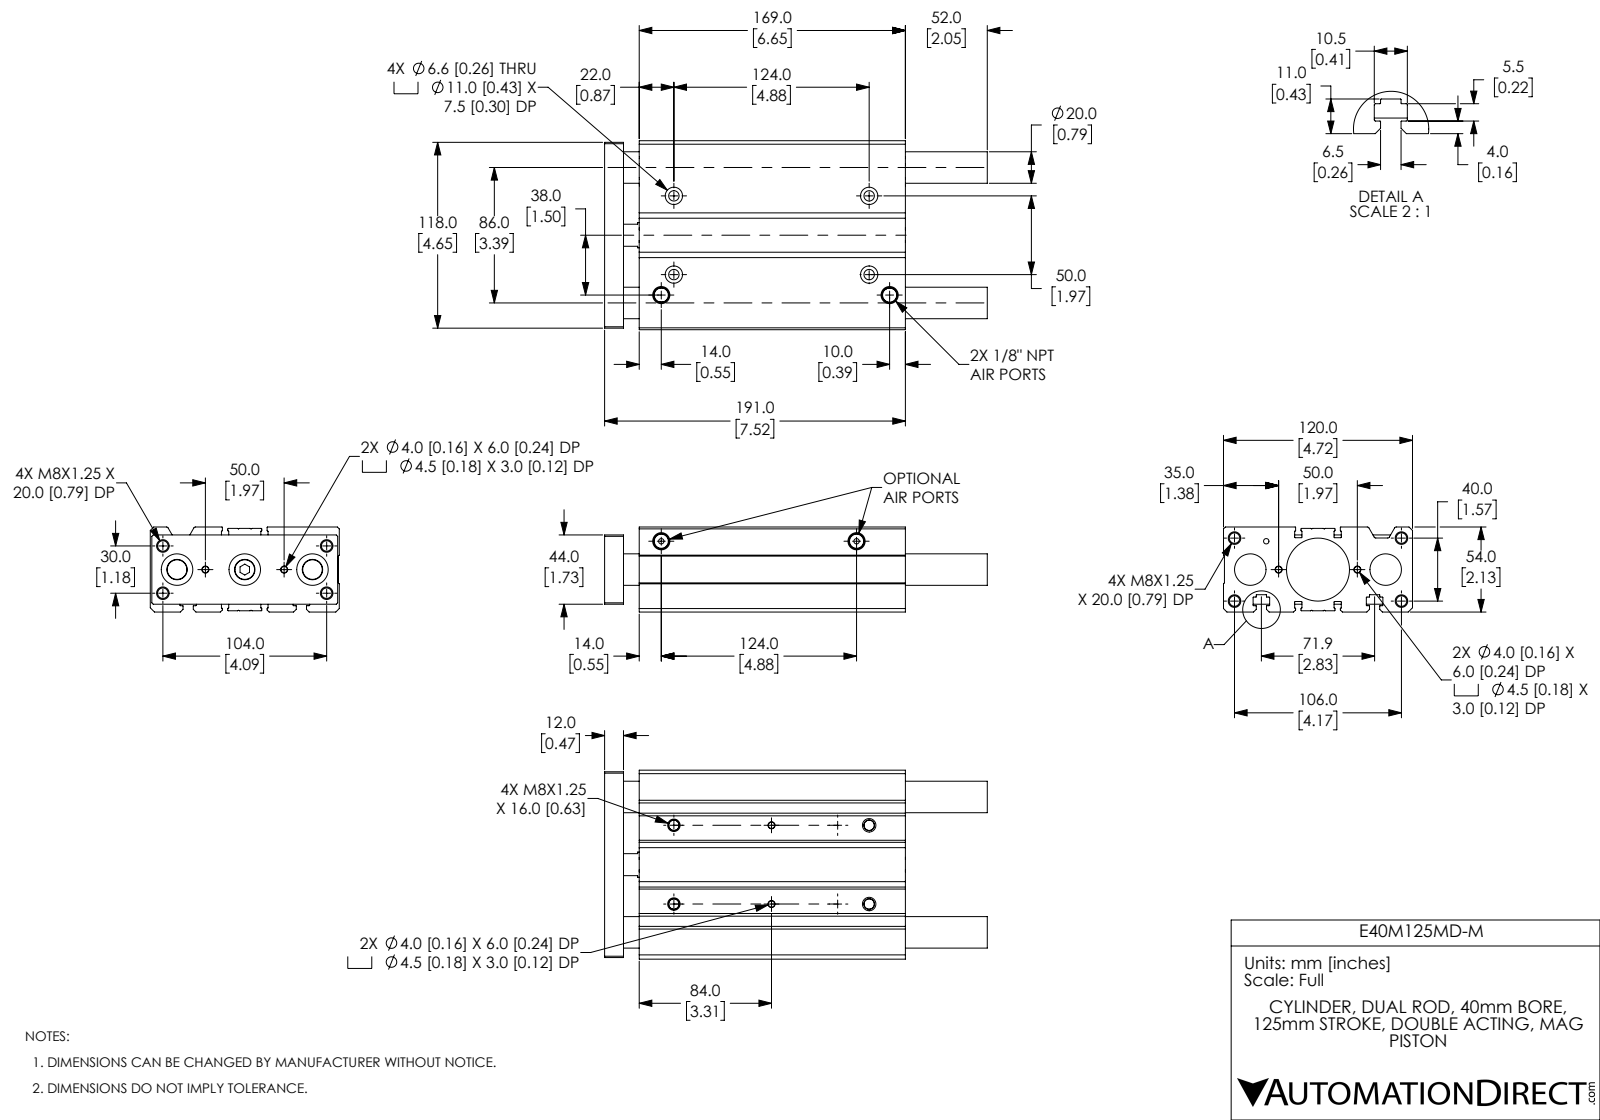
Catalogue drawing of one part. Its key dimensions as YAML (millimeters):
part_name: "E40M125MD-M_BODY; E40M125MD-M; E40M125MD-M_ENDPLATE"
step_written_by: "SolidWorks 2019 (CONFIG_CONTROL_DESIGN)"
units: millimeters
bodies: {solids: 5, faces: 427, planar: 139, cylindrical: 194, other: 94}
overall_size: [243, 120, 54]
volume: 966858
surface_area: 202635
round_holes:
  - {diameter: 6.65, count: 12}
  - {diameter: 4, count: 4}
  - {diameter: 4.5, count: 4}
  - {diameter: 6.6, count: 4}
  - {diameter: 11, count: 4}
  - {diameter: 3.43, count: 3}
  - {diameter: 10, count: 3}
  - {diameter: 20, count: 3}
  - {diameter: 10.91, count: 2}
  - {diameter: 12.95, count: 2}
  - {diameter: 20, count: 1}
  - {diameter: 40, count: 1}
round_bosses_or_shafts:
  - {diameter: 16, count: 1}
  - {diameter: 12.95, count: 1}
partial_cylinders:
  - {radius: 0.2, count: 32}
  - {radius: 0.4, count: 28}
  - {radius: 1.2, count: 4}
  - {radius: 0.3, count: 2}
face_to_face_distances: [54, 120, 22, 0.6, 12, 10, 191, 179, 169, 25]
hole_center_spacings: [5.1, 17.49, 22.36, 30.89, 34.41, 35.01, 50, 54.12]
